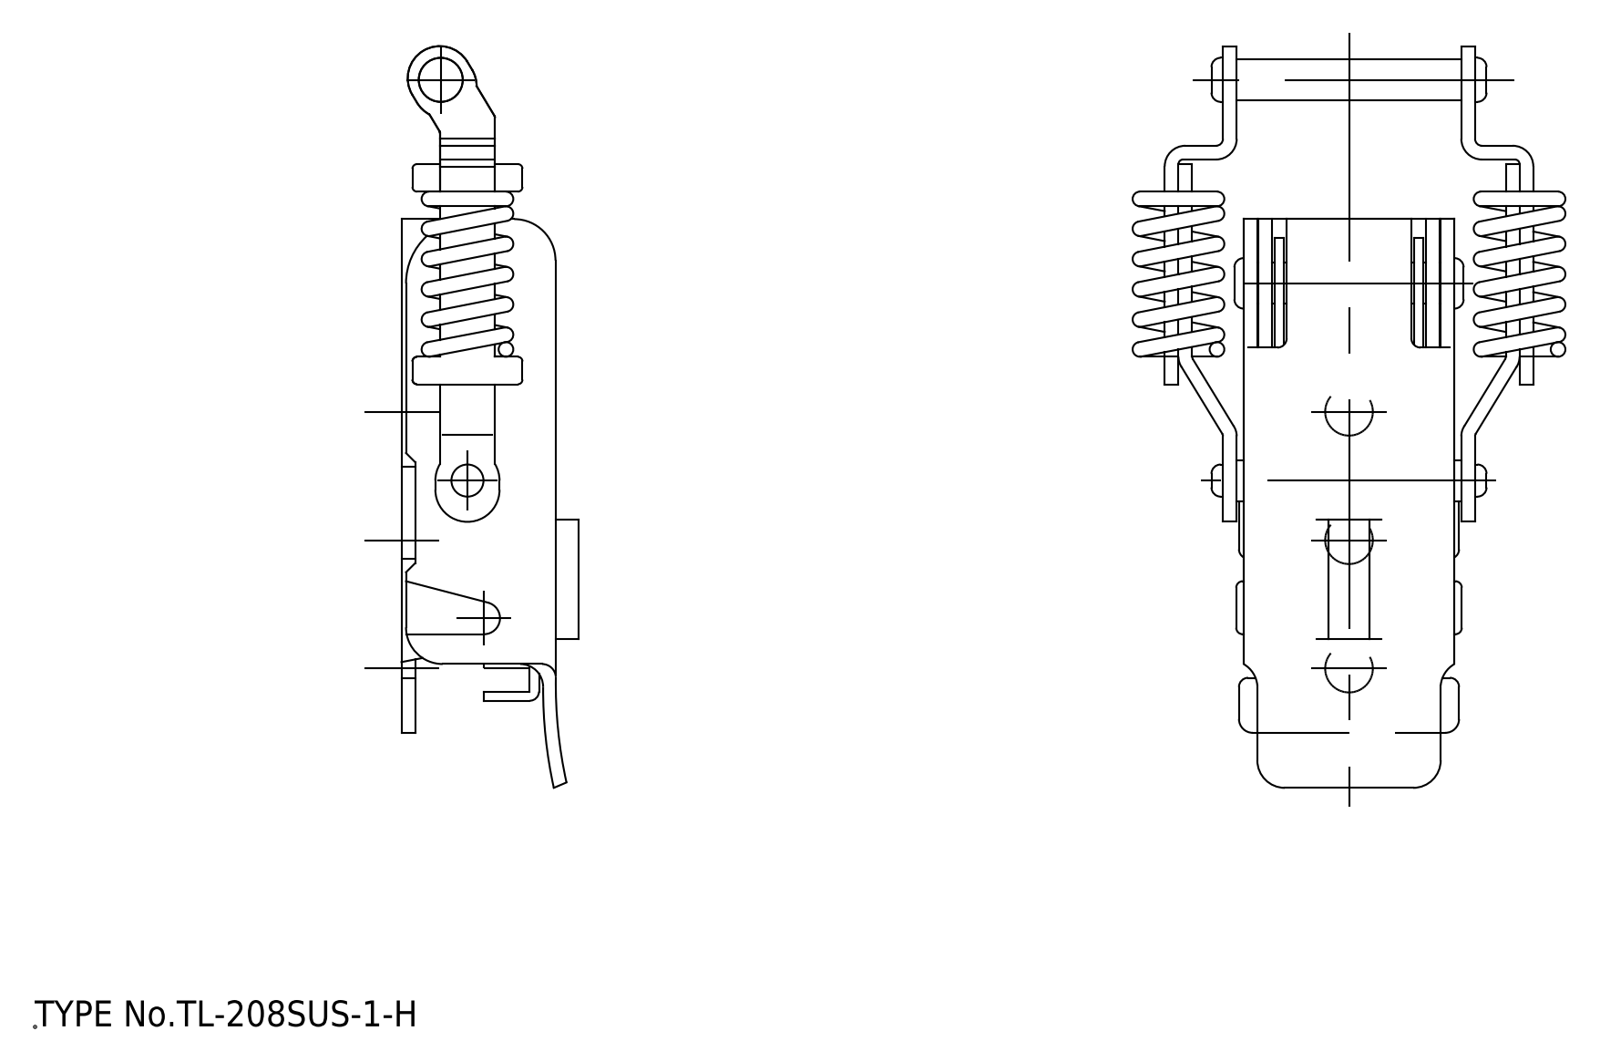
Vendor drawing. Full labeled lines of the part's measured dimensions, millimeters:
Part name (STEP PRODUCT): アーム(A); アーム(B); ベース; レバー(A) (+2 more)
STEP written by: spGate 19.8.4 (****-****-****-****) (AUTOMOTIVE_DESIGN)
Units: millimetres
Bodies: 7 solids, 459 faces (201 planar, 154 cylindrical, 104 other)
Overall size (bounding box): 80.93 × 47.2 × 19.3
Volume: 11 473 mm³ · Surface area: 18 152 mm²
Round holes (diameter × count): ⌀5.2 ×3, ⌀5.5 ×2, ⌀4.5 ×1
Round bosses / shafts (diameter × count): ⌀4.5 ×2, ⌀4.8 ×1, ⌀4 ×1, ⌀3.5 ×1, ⌀2.5 ×1
Partial cylindrical surfaces — rounded edges, fillets, slot ends (radius × count): R0.5 ×18, R1 ×15, R3 ×8, R1.5 ×7, R2.25 ×5, R0.7 ×4, R2 ×4, R3.5 ×4
Main face-to-face distances: 1.5, 15.3, 1, 21.5, 1.6, 19.9, 16.8, 1.8, 1.3, 2.8
Hole centre spacings: 14, 21.68, 28
